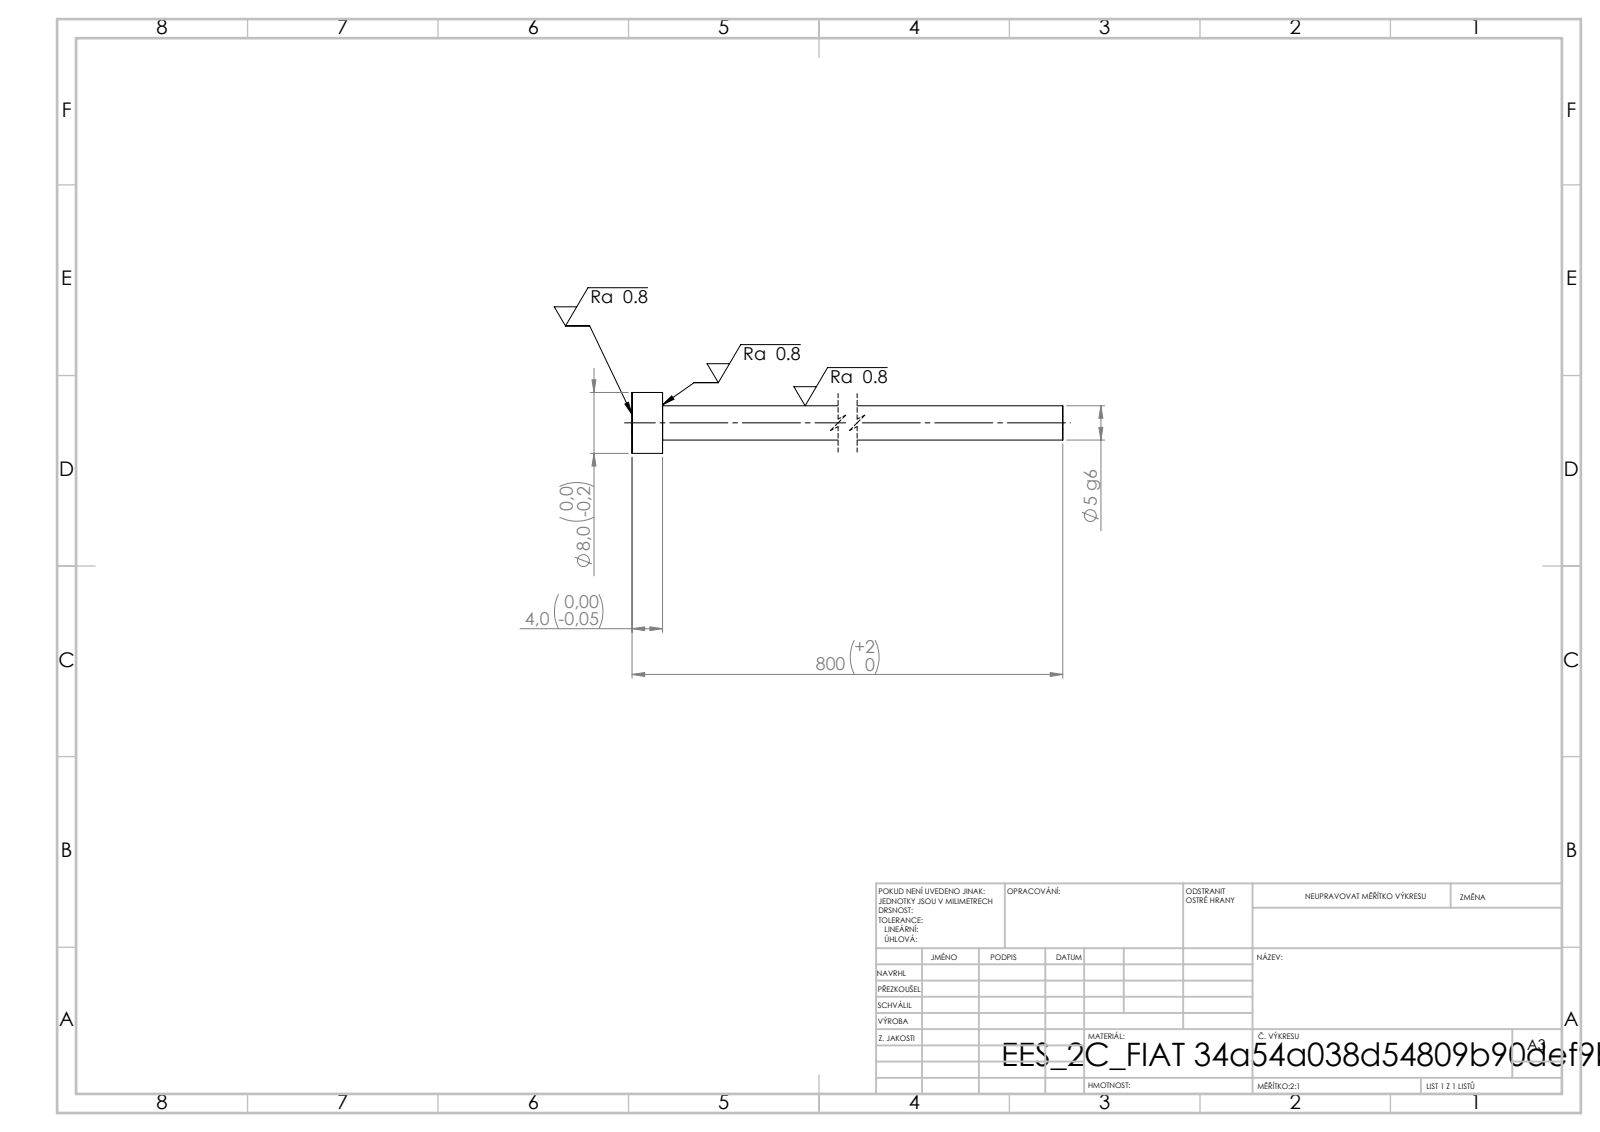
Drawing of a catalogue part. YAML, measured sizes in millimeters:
step_written_by: "SolidWorks 2019 (CONFIG_CONTROL_DESIGN)"
units: millimeters
bodies: {solids: 1, faces: 7, planar: 3, cylindrical: 4, other: 0}
overall_size: [800, 8, 8]
volume: 12861
surface_area: 11454
round_bosses_or_shafts:
  - {diameter: 8, count: 1}
  - {diameter: 4.5, count: 1}
face_to_face_distances: [4, 800, 796]
